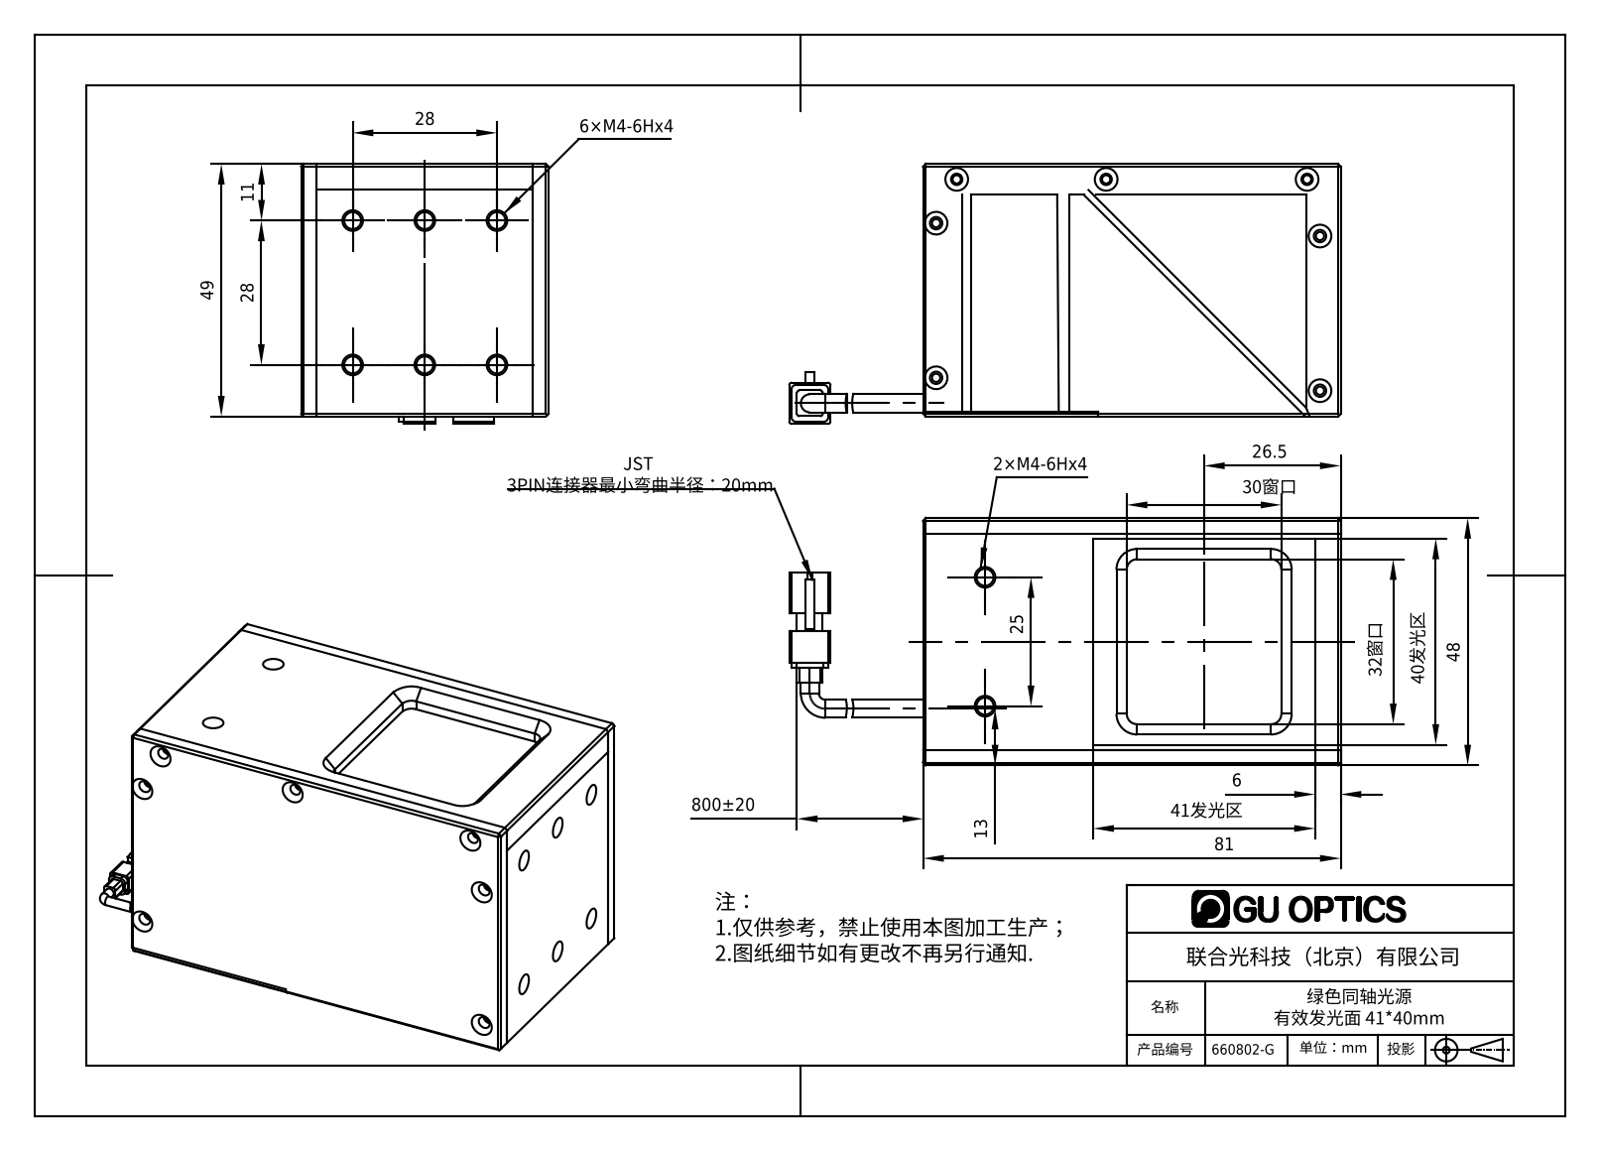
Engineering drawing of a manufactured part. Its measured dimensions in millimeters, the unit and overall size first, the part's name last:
Units: millimetres
Overall size (bounding box): 95 × 49 × 48
Round holes (diameter × count): ⌀1.6 ×12, ⌀4 ×12, ⌀2.4 ×8, ⌀3.3 ×8, ⌀2 ×4, ⌀2.2 ×3
Round bosses / shafts (diameter × count): ⌀1.75 ×2
Partial cylindrical surfaces — rounded edges, fillets, slot ends (radius × count): R0.5 ×8, R1 ×4, R2 ×4, R1.65 ×1, R5 ×1
Main face-to-face distances: 1, 4, 44, 48, 3, 2, 45, 41, 42, 6
Hole centre spacings: 28, 14, 31.3, 10.82, 15.7, 20.12, 21.78, 24
Volume: 67 117 mm³ · Surface area: 51 801 mm²
Bodies: 11 solids, 631 faces (315 planar, 156 cylindrical, 160 other)
Part name (STEP PRODUCT): 绿色同轴光源 有效发光面 4140mm
STEP written by: SolidWorks 2016 (AUTOMOTIVE_DESIGN)
